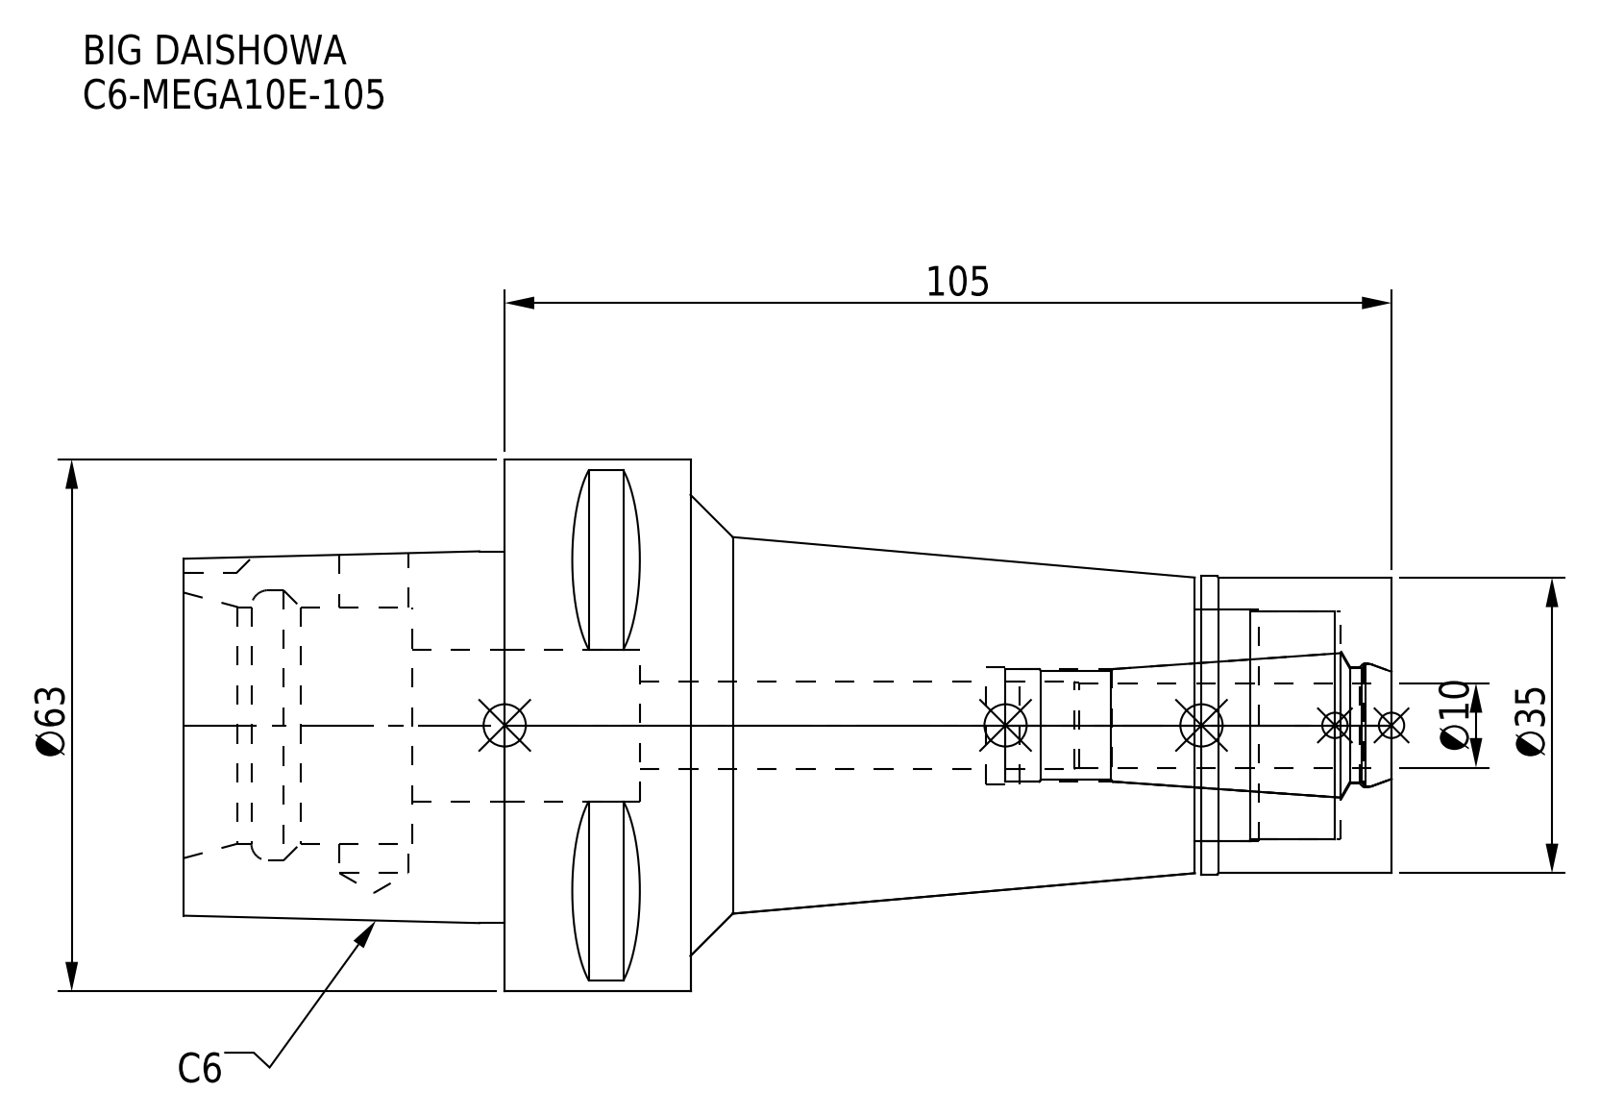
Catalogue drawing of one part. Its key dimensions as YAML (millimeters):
part_name: "C6-MEGA10E-105-100.stp; C6-MEGA10E-105-100_ASM.stp; C6-MEGA10E-105; DXF_TEMP_ASSY_ASM_4_ASM.stp (+3 more)"
step_written_by: "SolidWorks 2019 (CONFIG_CONTROL_DESIGN)"
units: millimeters
bodies: {solids: 2, faces: 97, planar: 36, cylindrical: 37, other: 24}
overall_size: [143, 63, 63]
volume: 184985
surface_area: 36946
round_holes:
  - {diameter: 8.1, count: 1}
  - {diameter: 10.4, count: 1}
  - {diameter: 13.3, count: 1}
  - {diameter: 13.8, count: 1}
  - {diameter: 13.9, count: 1}
  - {diameter: 14.7, count: 1}
  - {diameter: 18, count: 1}
  - {diameter: 27, count: 1}
  - {diameter: 27.5, count: 1}
  - {diameter: 28, count: 1}
  - {diameter: 32, count: 1}
round_bosses_or_shafts:
  - {diameter: 63, count: 1}
  - {diameter: 35.3, count: 1}
  - {diameter: 35, count: 1}
partial_cylinders:
  - {radius: 5, count: 1}
face_to_face_distances: [83, 105, 22, 27, 38, 6, 143, 60, 22.5, 60.5]
